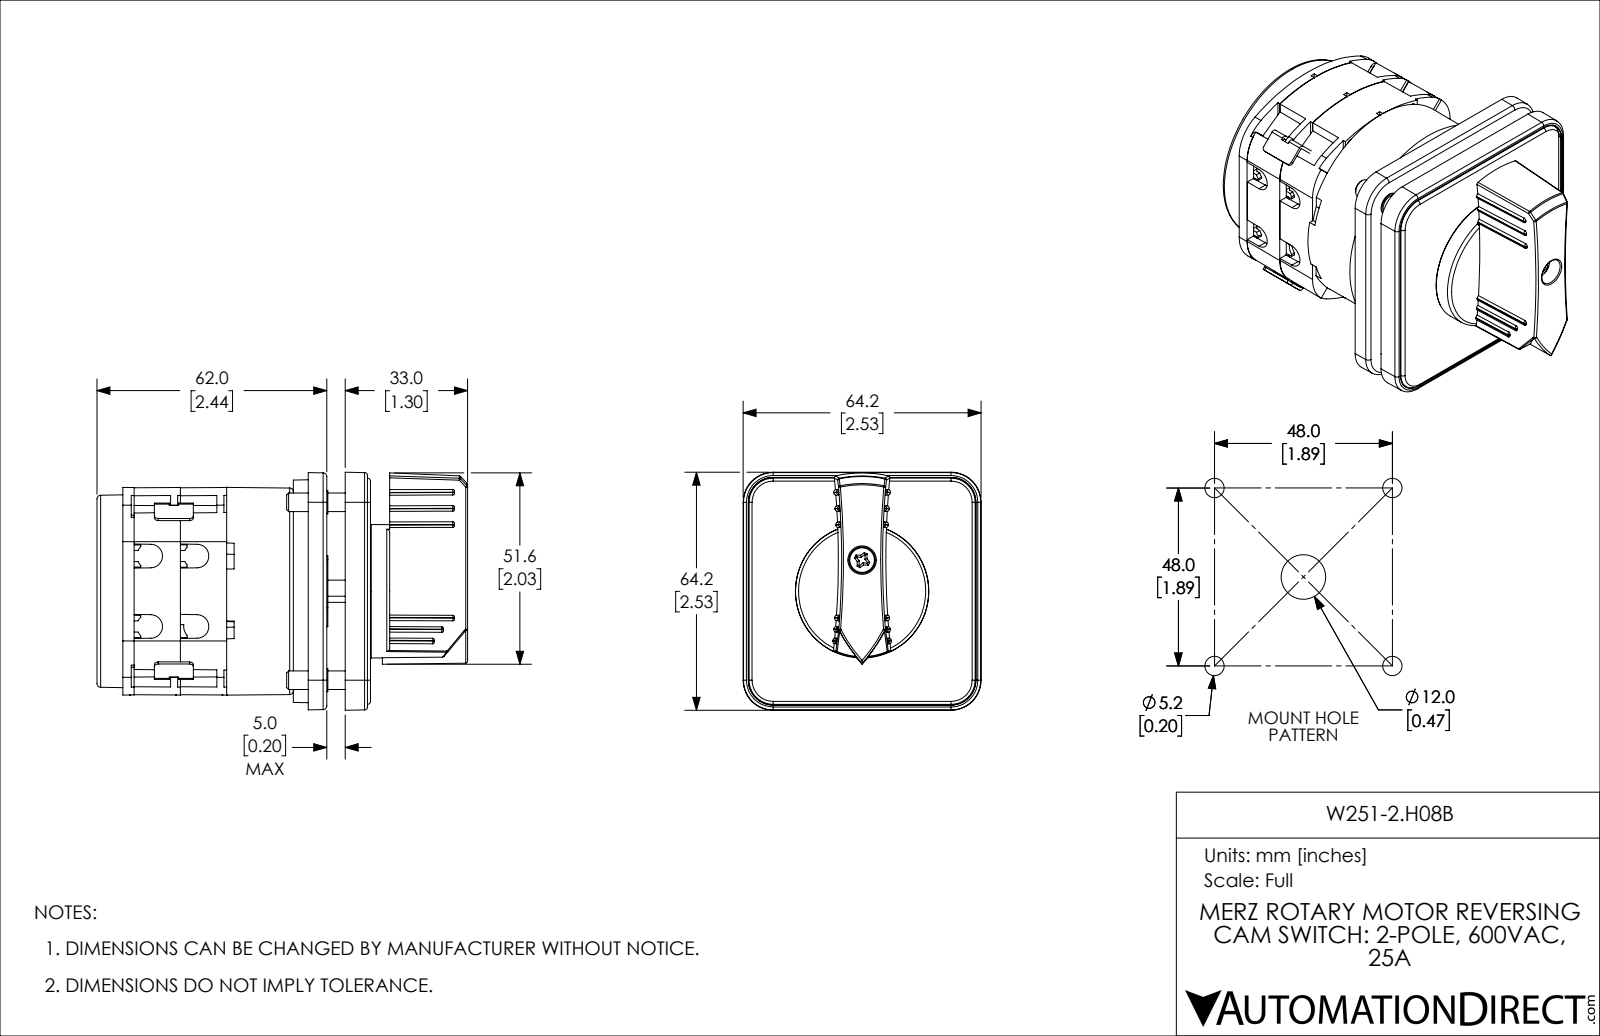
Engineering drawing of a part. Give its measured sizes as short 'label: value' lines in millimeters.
name: W251-2.H08B
written by: SolidWorks 2019 (CONFIG_CONTROL_DESIGN)
unit: mm
bodies: 13 solids, 2915 faces (1688 planar, 249 cylindrical, 978 other)
size: 100 × 64.2 × 64.2
volume: 163 600 mm³; area: 89 230 mm²
holes: 6× ⌀8, 4× ⌀0.3, 4× ⌀4, 4× ⌀5, 4× ⌀5.2, 4× ⌀9.5, 1× ⌀13, 1× ⌀23.5
bosses: 4× ⌀9.3, 4× ⌀8.1, 4× ⌀7.3, 4× ⌀5, 1× ⌀7.5, 1× ⌀3.5
rounds: 21× R1, 14× R0.2, 11× R0.8, 6× R0.5, 4× R0.1, 4× R0.2, 4× R0.5, 4× R0.9
face distances: 10, 12.5, 11.8, 1.8, 0.8, 18.2, 19, 5, 9, 20.8
hole spacings: 42.4, 8.5, 9, 9.3, 9.5, 16.4, 16.5, 18.1
